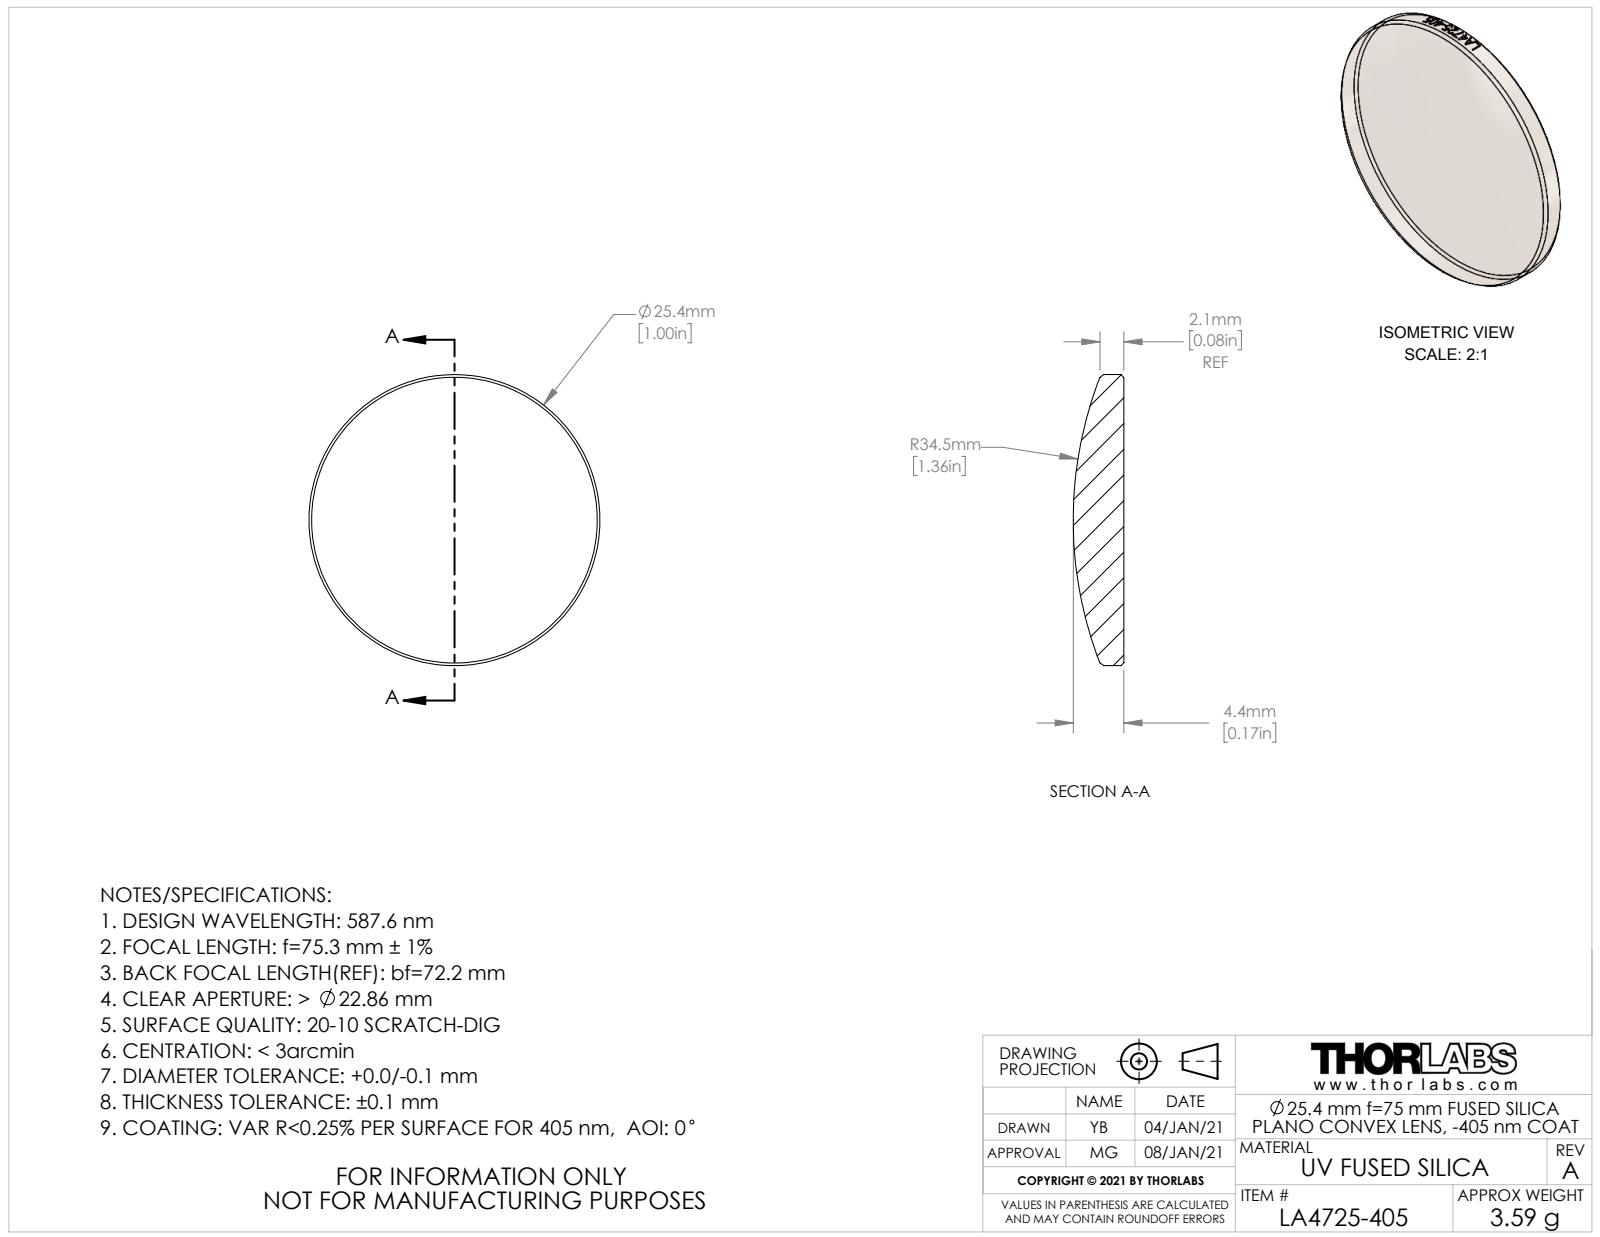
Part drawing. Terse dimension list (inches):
name: CTN016814-E0W; CTN016834
written by: SolidWorks 2018 (AUTOMOTIVE_DESIGN)
unit: in
bodies: 1 solid, 28 faces (1 planar, 21 cylindrical, 6 other)
size: 1 × 1 × 0.174
volume: 0.099 in³; area: 1.818 in²
bosses: 1× ⌀1
